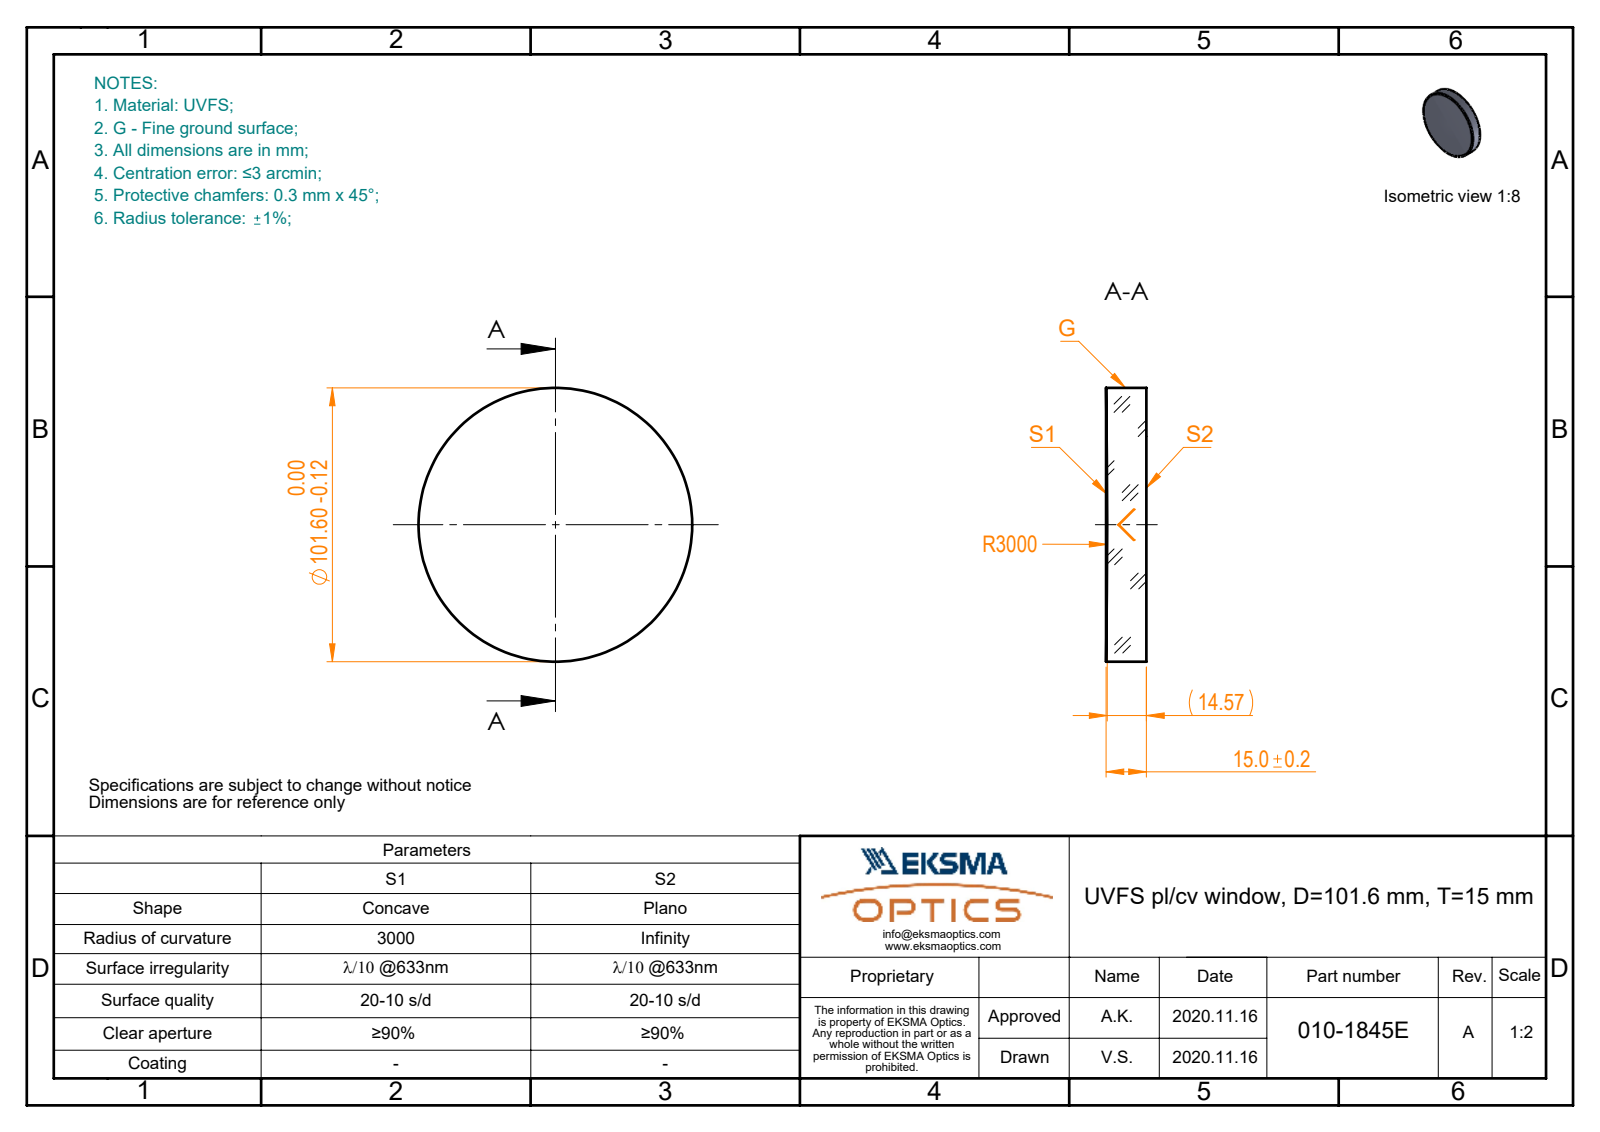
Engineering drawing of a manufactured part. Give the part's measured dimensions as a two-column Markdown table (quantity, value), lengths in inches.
| quantity | value |
| --- | --- |
| part name | 010-1845E_UVFS_PCV_window |
| STEP written by | SolidWorks 2019 (CONFIG_CONTROL_DESIGN) |
| units | inches |
| bodies | 1 solid, 5 faces (1 planar, 2 cylindrical, 2 other) |
| overall size | 4 × 4 × 0.591 |
| volume | 7.315 in³ |
| surface area | 32.55 in² |
| round bosses / shafts (diameter × count) | 4 × 1 |
